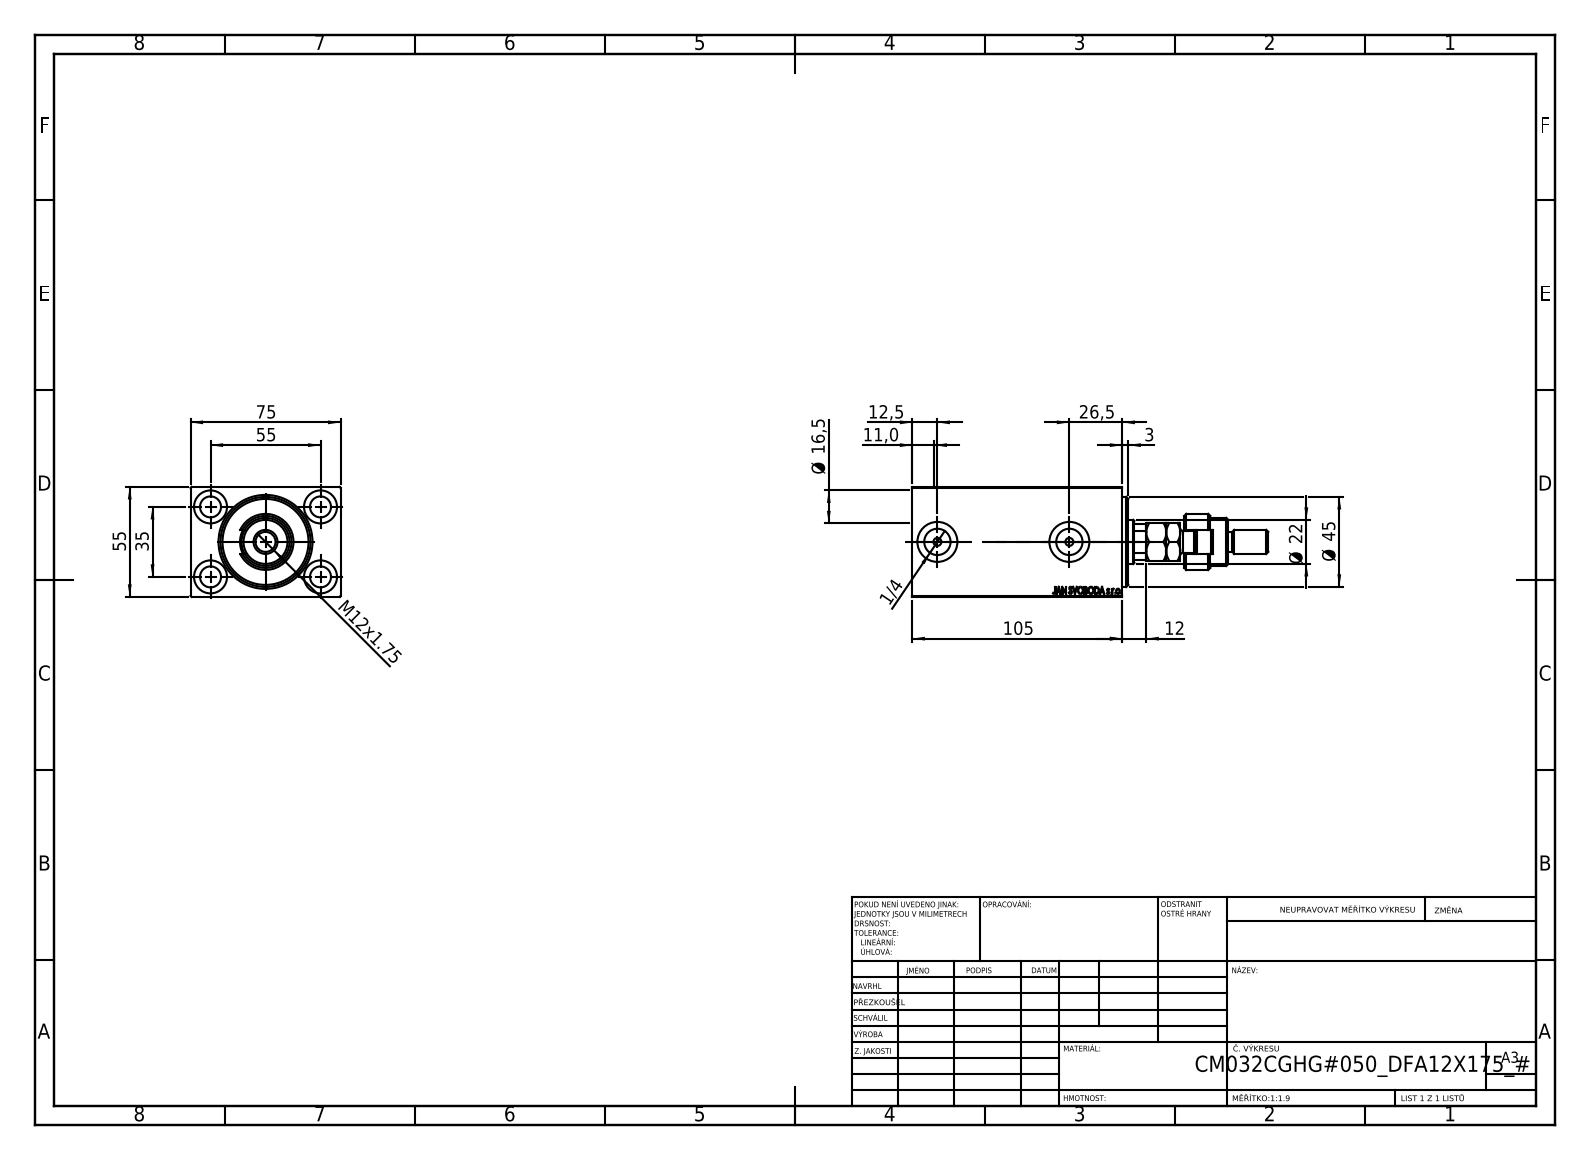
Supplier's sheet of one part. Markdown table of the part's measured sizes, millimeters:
| quantity | value |
| --- | --- |
| part name | V450CM_C_Body; V450CM_C_VCP; V450CM_VC_B; FEMALE_PART_FOR_DFA (+1 more) |
| STEP written by | SolidWorks 2019 (CONFIG_CONTROL_DESIGN) |
| units | millimeters |
| bodies | 5 solids, 947 faces (436 planar, 73 cylindrical, 438 other) |
| overall size | 178 × 75 × 55 |
| volume | 384 189 mm³ |
| surface area | 84 302 mm² |
| round holes (diameter × count) | 10.5 × 5, 16.5 × 4, 4 × 2, 13.16 × 2, 20 × 2, 22 × 1, 25.5 × 1, 32 × 1, 34 × 1, 45 × 1 |
| round bosses / shafts (diameter × count) | 28 × 1, 24 × 1, 18 × 1, 12 × 1, 11 × 1, 10 × 1 |
| partial cylindrical surfaces (radius × count) | 9.75 × 1, 10.5 × 1 |
| main face-to-face distances | 55, 75, 10, 95, 105, 8, 100, 5, 90, 12 |
| hole center spacings | 32.6, 35, 55, 65.19, 66 |
